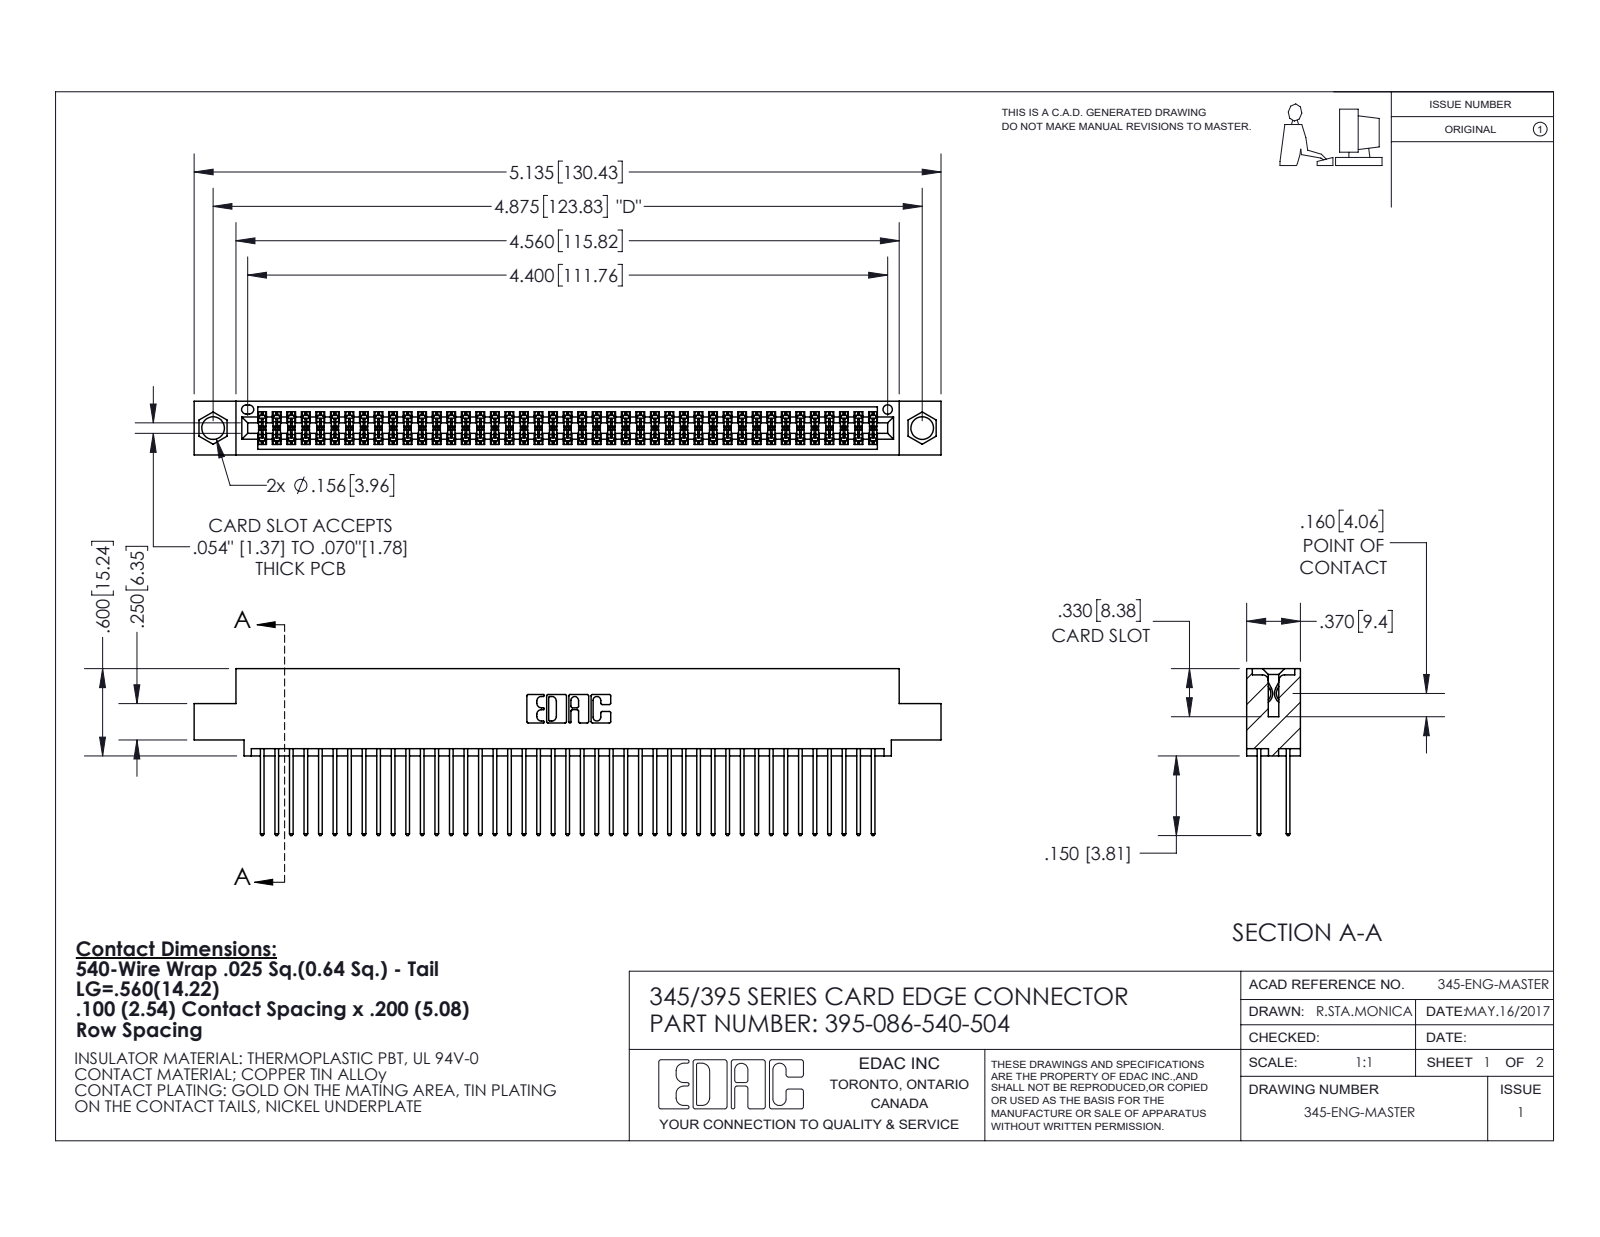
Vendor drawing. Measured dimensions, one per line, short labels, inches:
name: 395-086-540-504; 345-292-001_345-293-140; 345 Part_0.110 Offset - 0.156 Dia-TI
written by: SolidWorks 2020 (CONFIG_CONTROL_DESIGN)
unit: in
bodies: 87 solids, 4444 faces (2936 planar, 1508 cylindrical, 0 other)
size: 5.135 × 1.147 × 0.37
volume: 0.783 in³; area: 31.67 in²
holes: 2× ⌀0.156, 1× ⌀0.064
rounds: 129× R0.006, 86× R0.01, 22× R0.01, 6× R0.007, 6× R0.031, 3× R0.026, 2× R0.014, 2× R0.019
face distances: 0.298, 0.072, 0.2, 0.098, 0.272, 0.025, 0.37, 0.225, 0.175, 0.149
hole spacings: 0.27, 4.639, 4.875
